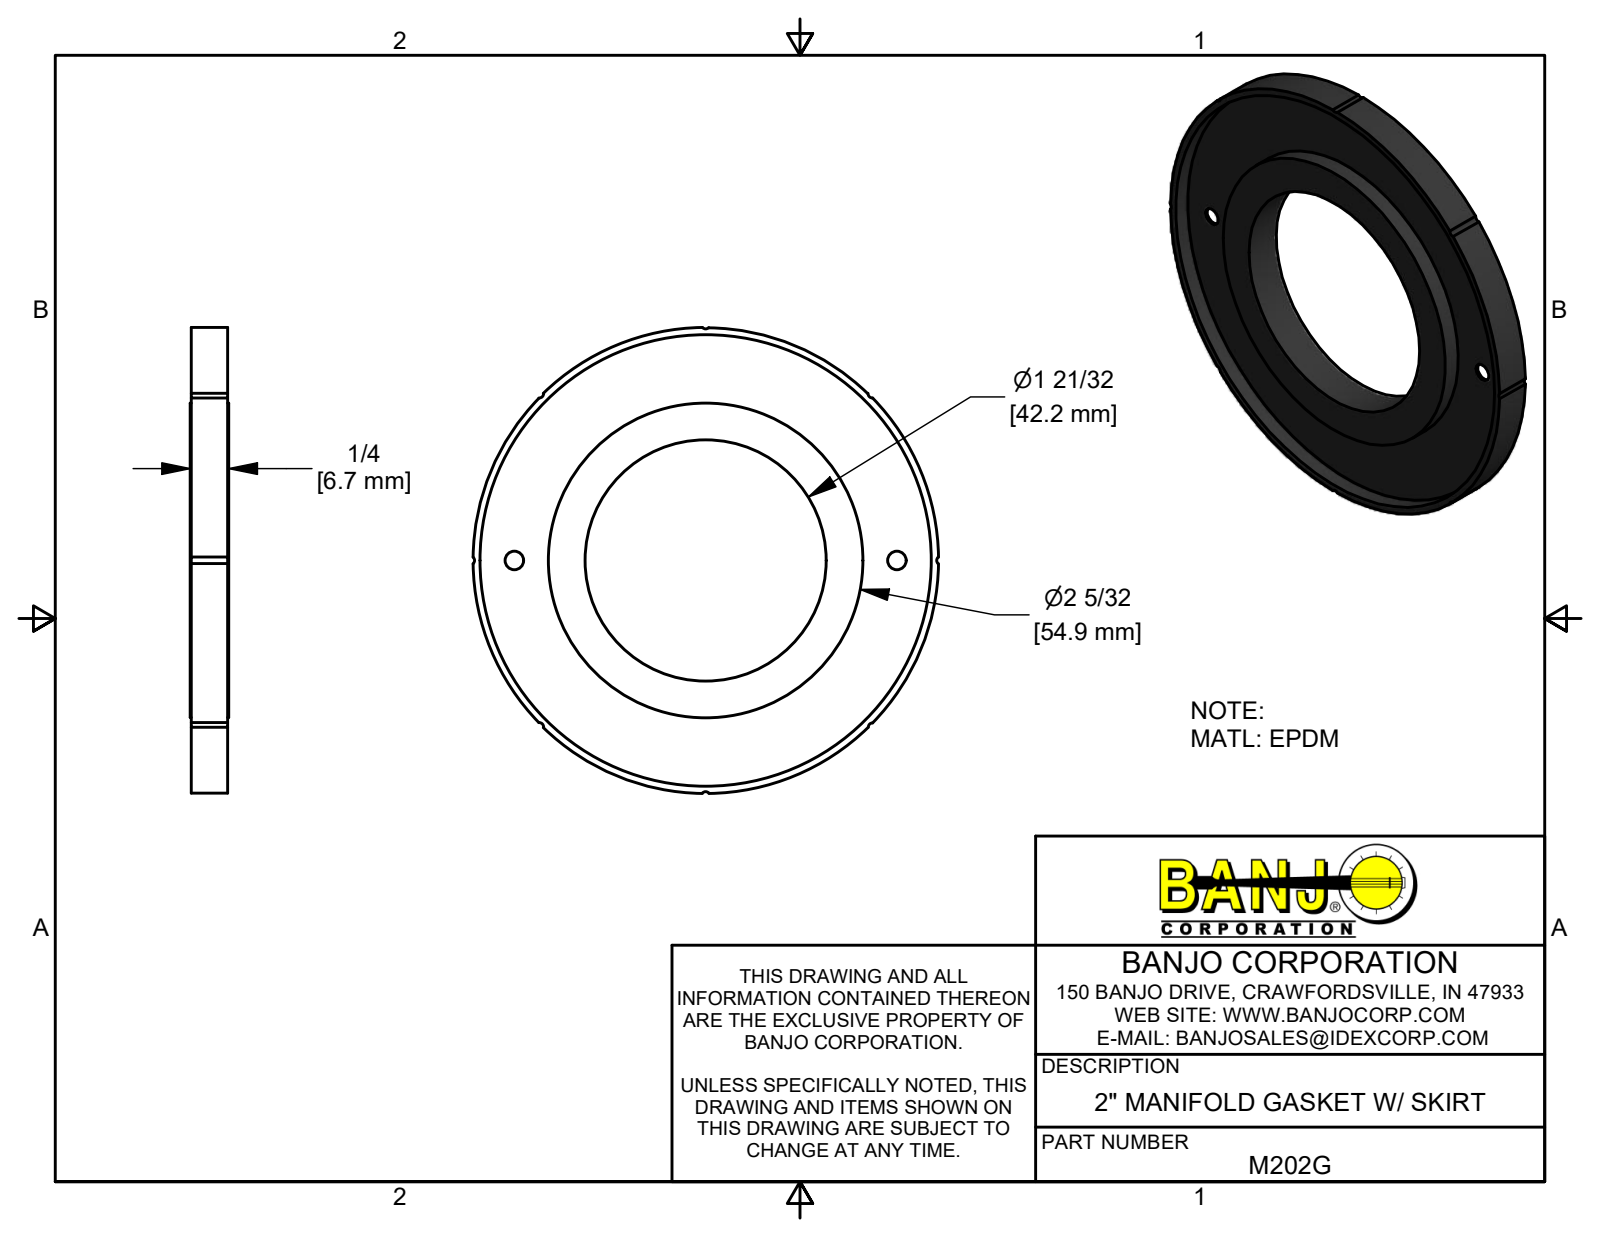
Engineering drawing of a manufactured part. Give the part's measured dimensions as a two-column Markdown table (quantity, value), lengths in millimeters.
| quantity | value |
| --- | --- |
| part name | M202G |
| STEP written by | Autodesk Inventor 2019 (AUTOMOTIVE_DESIGN) |
| units | millimeters |
| bodies | 1 solid, 29 faces (6 planar, 23 cylindrical, 0 other) |
| overall size | 81.3 × 81.3 × 6.7 |
| volume | 9 540 mm³ |
| surface area | 12 640 mm² |
| round holes (diameter × count) | 3.2 × 2, 42.2 × 1, 78.7 × 1 |
| round bosses / shafts (diameter × count) | 81.3 × 1, 54.9 × 1 |
| partial cylindrical surfaces (radius × count) | 0.8 × 8 |
| main face-to-face distances | 0.4, 3.1, 3.6, 6.7, 6.5, 3, 3.4, 6.4 |
| hole center spacings | 33.4, 66.8 |
